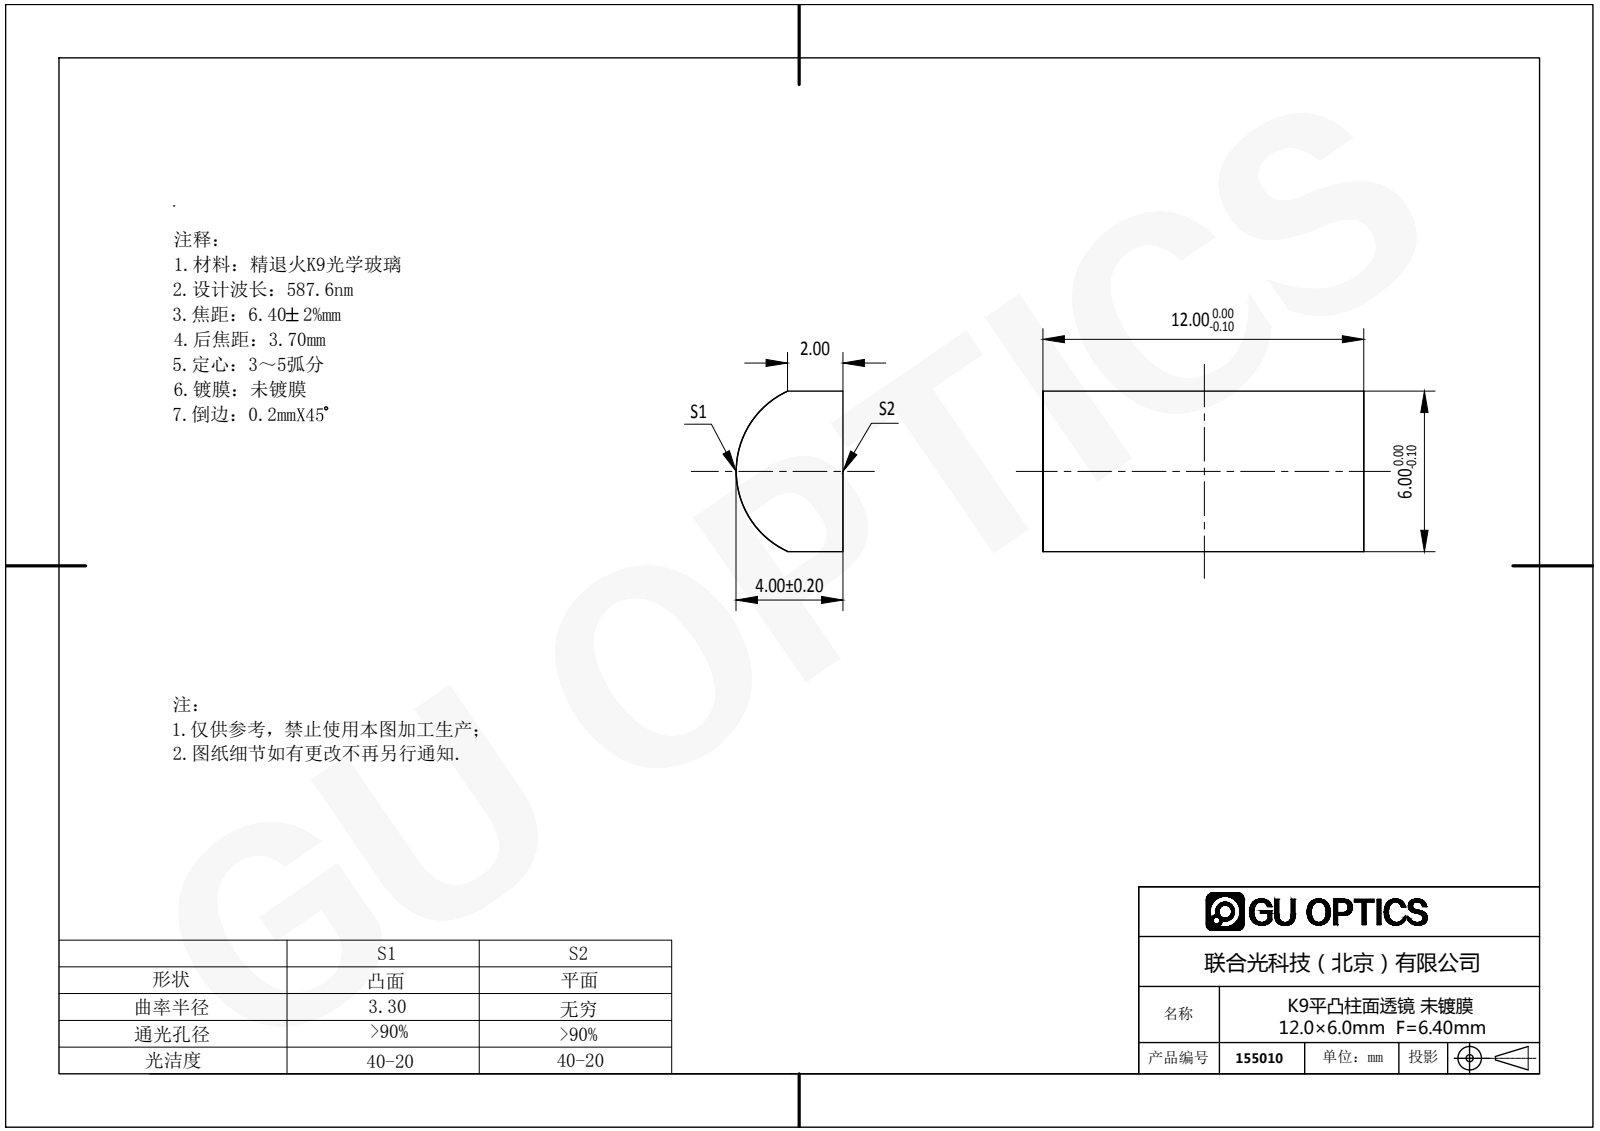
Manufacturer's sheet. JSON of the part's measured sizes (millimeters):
{"part_name": "155010", "step_written_by": "SolidWorks 2016 (AUTOMOTIVE_DESIGN)", "units": "millimeters", "bodies": {"solids": 1, "faces": 6, "planar": 5, "cylindrical": 1, "other": 0}, "overall_size": [12, 6, 4], "volume_mm3": 249, "surface_area_mm2": 254, "partial_cylinders_radius": [[3.3, 1]], "face_to_face_distances": [6, 12]}
